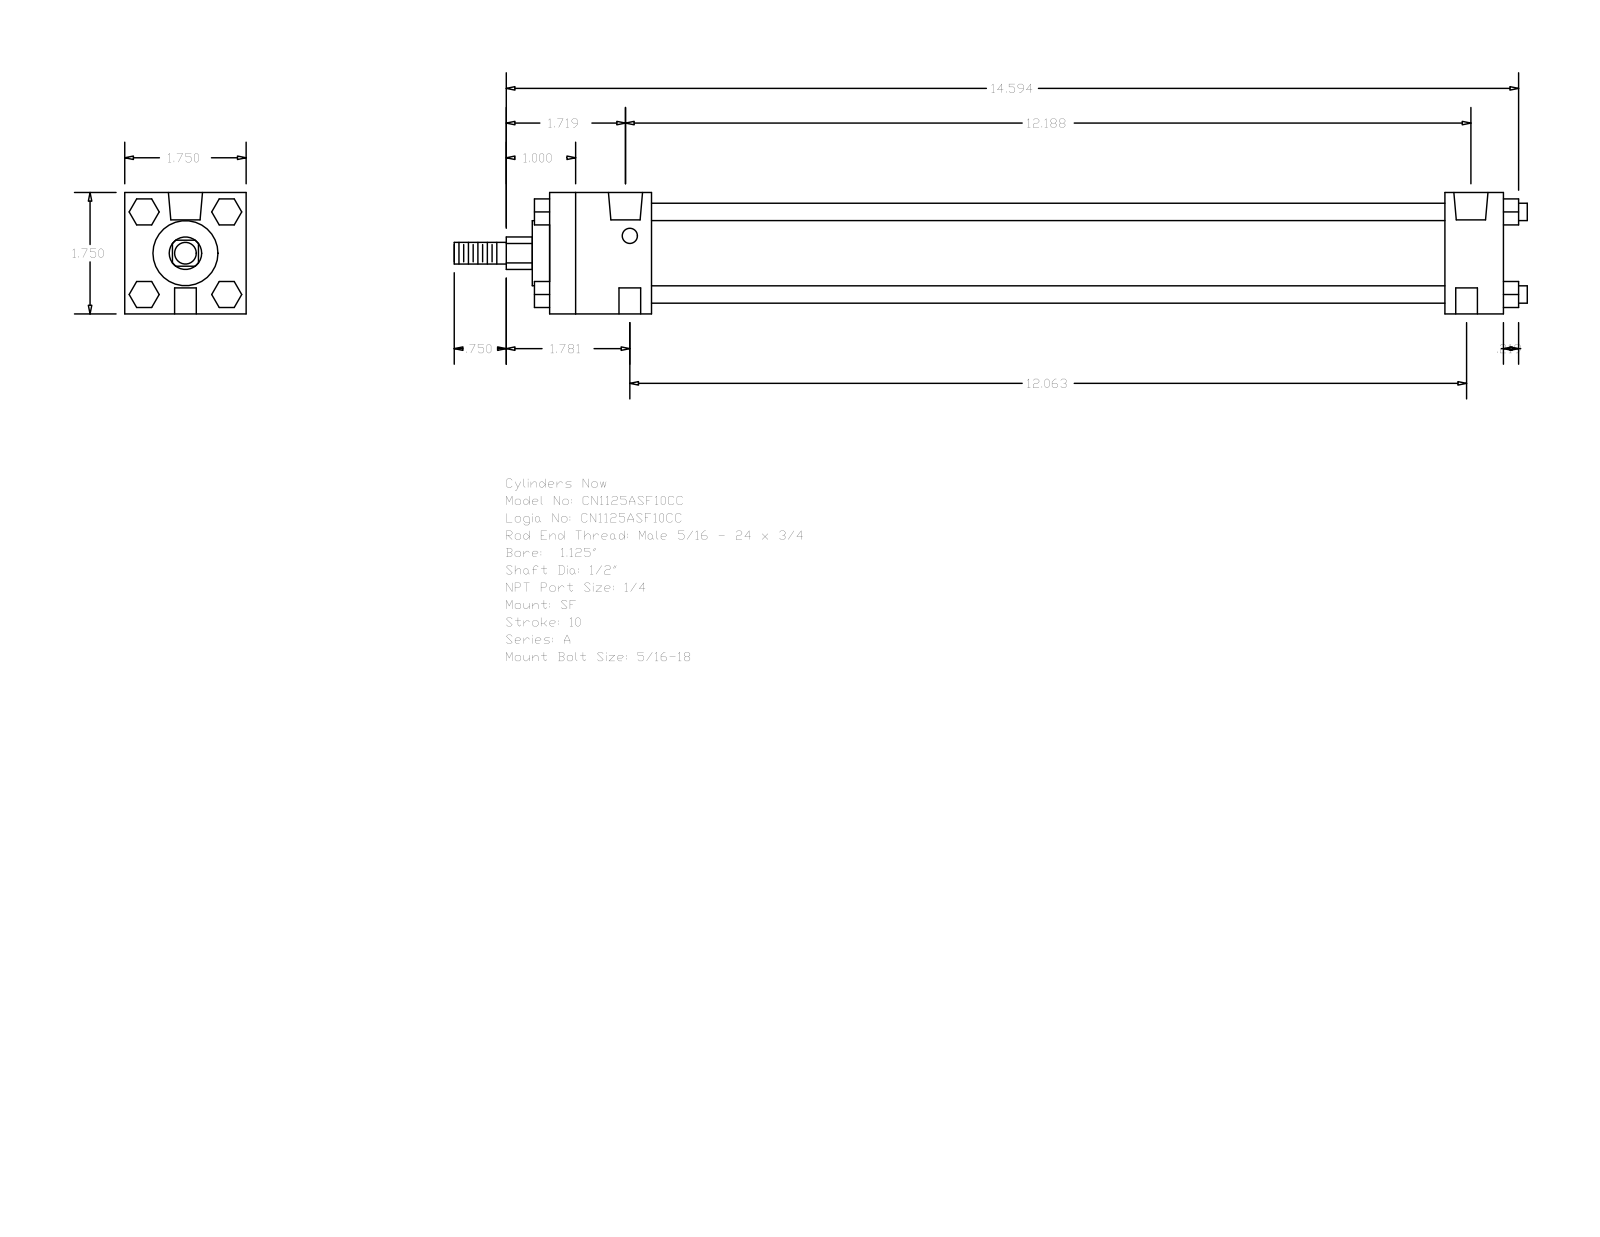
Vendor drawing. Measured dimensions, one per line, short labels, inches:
name: A_SF__0112_0.5
written by: GSSL Pune (CONFIG_CONTROL_DESIGN)
unit: in
bodies: 0 solids, 120 faces (92 planar, 28 cylindrical, 0 other)
size: 15.469 × 1.75 × 1.75
holes: 2× ⌀0.219, 2× ⌀0.313, 2× ⌀0.492
bosses: 4× ⌀0.25, 1× ⌀1.255, 1× ⌀0.937, 1× ⌀0.5, 1× ⌀0.313
rounds: 1× R0.234
face distances: 1.75, 13.75, 12.906, 0.844, 1.469, 11.437, 12.281, 0.375, 0.22, 0.219
hole spacings: 12.063, 0.062, 0.063, 12.125, 12.125, 12.187
